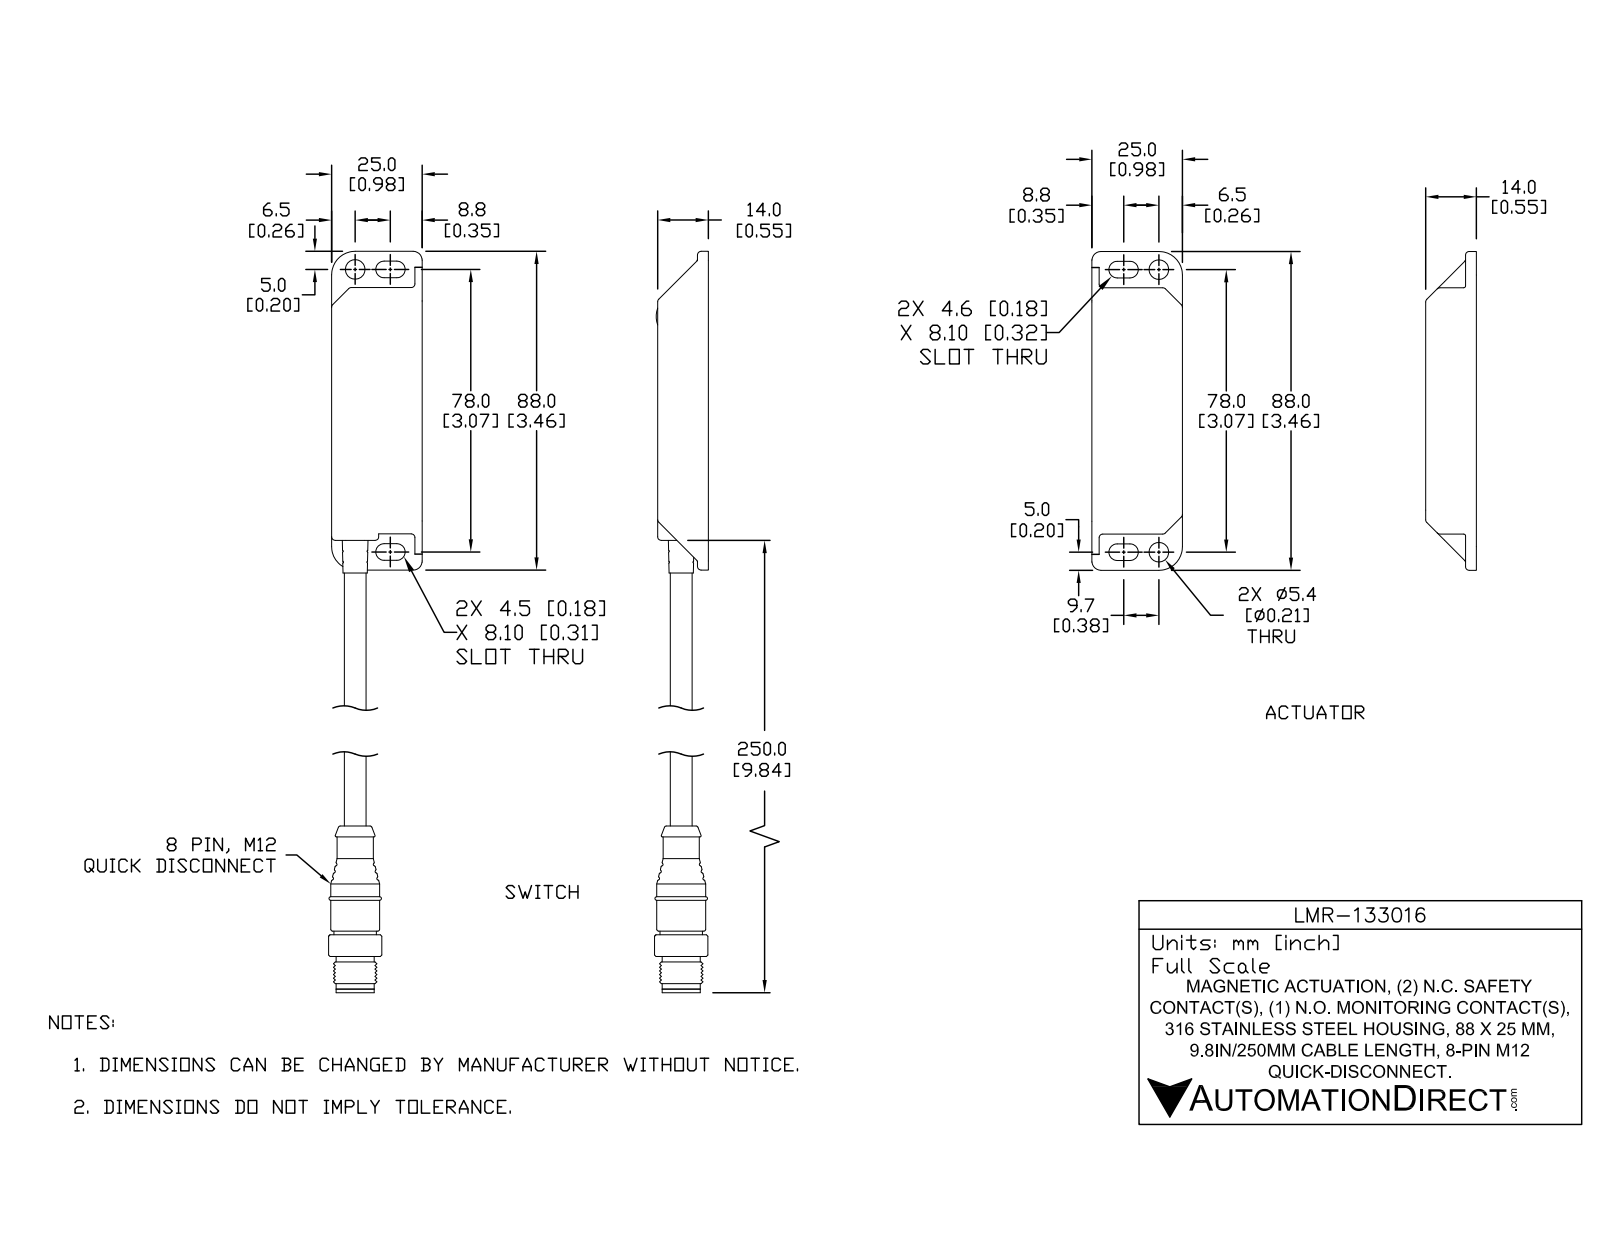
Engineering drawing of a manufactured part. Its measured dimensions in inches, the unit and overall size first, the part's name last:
Units: inches
Overall size (bounding box): 12.984 × 2.041 × 0.585
Round holes (diameter × count): ⌀0.197 ×4, ⌀0.213 ×4, ⌀0.232 ×1, ⌀0.283 ×1, ⌀0.327 ×1, ⌀0.465 ×1
Round bosses / shafts (diameter × count): ⌀0.031 ×8, ⌀0.079 ×4, ⌀0.193 ×2, ⌀0.134 ×2, ⌀0.531 ×1, ⌀0.461 ×1, ⌀0.413 ×1, ⌀0.394 ×1
Partial cylindrical surfaces — rounded edges, fillets, slot ends (radius × count): R0.02 ×95, R0.039 ×45, R0.091 ×8, R0.098 ×4, R0.256 ×4, R0.193 ×1, R0.289 ×1
Main face-to-face distances: 0.067, 0.055, 1.024, 0.543, 0.476, 0.421, 0.488, 0.917, 0.039, 0.106
Hole centre spacings: 0.67, 1.172, 1.181, 1.243, 1.496, 1.687, 1.815, 1.907
Volume: 2.041 in³ · Surface area: 53.73 in²
Bodies: 11 solids, 1033 faces (351 planar, 356 cylindrical, 326 other)
Part name (STEP PRODUCT): LMR-133016; LMR-133016_1; LMR-133016_2
STEP written by: SolidWorks 2017 (AUTOMOTIVE_DESIGN)
